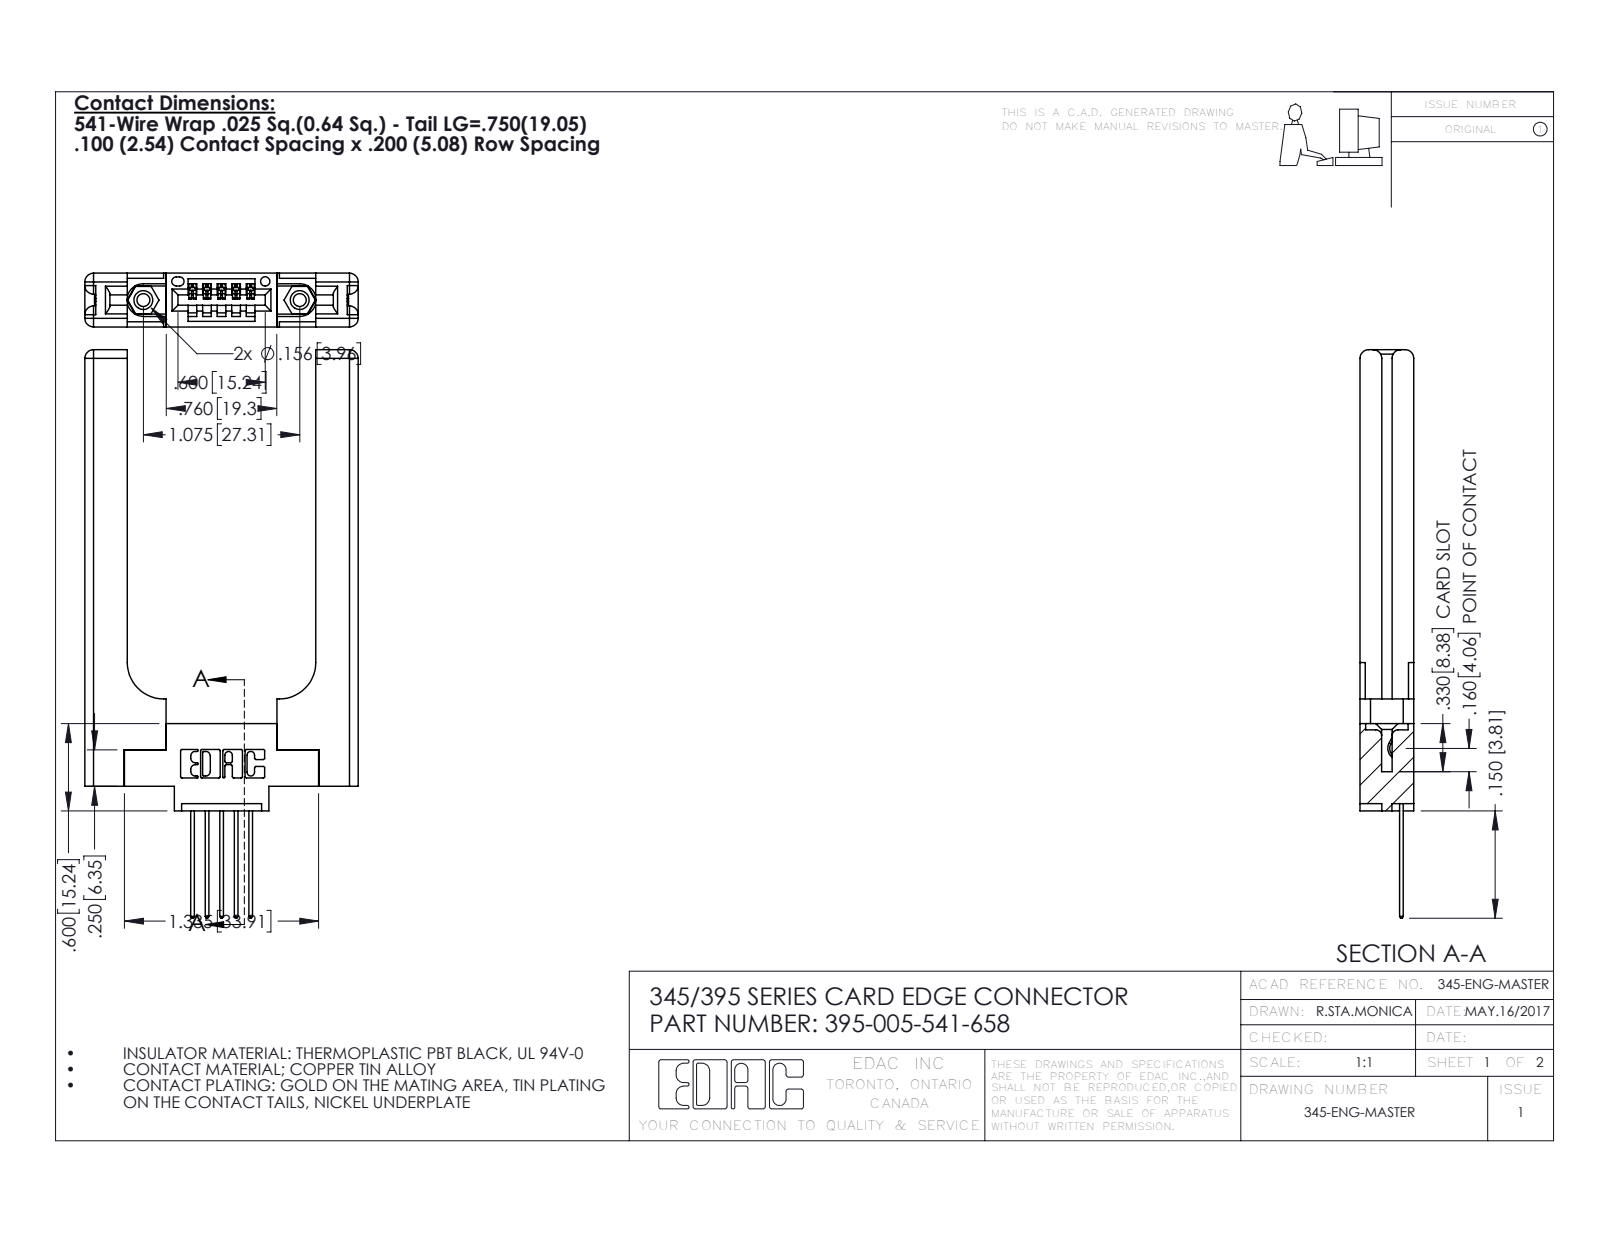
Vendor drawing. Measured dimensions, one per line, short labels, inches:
name: 345-250-001_345-250-001-102; 345-292-001_345-293-141; 345 Part_0.170 Offset - 0.156 Dia-TH; 345-220-058_345-220-058 (+1 more)
written by: SolidWorks 2016 (CONFIG_CONTROL_DESIGN)
unit: in
bodies: 10 solids, 676 faces (432 planar, 184 cylindrical, 60 other)
size: 3.907 × 1.879 × 0.37
volume: 0.771 in³; area: 16.3 in²
holes: 2× ⌀0.089, 2× ⌀0.125, 2× ⌀0.156, 1× ⌀0.064
bosses: 2× ⌀0.155
rounds: 22× R0.01, 16× R0.06, 10× R0.006, 10× R0.01, 6× R0.007, 6× R0.031, 3× R0.026, 2× R0.03
face distances: 0.37, 0.15, 0.22, 0.072, 1.296, 0.148, 0.077, 0.298, 0.071, 0.292
hole spacings: 0.27, 0.847, 1.075
